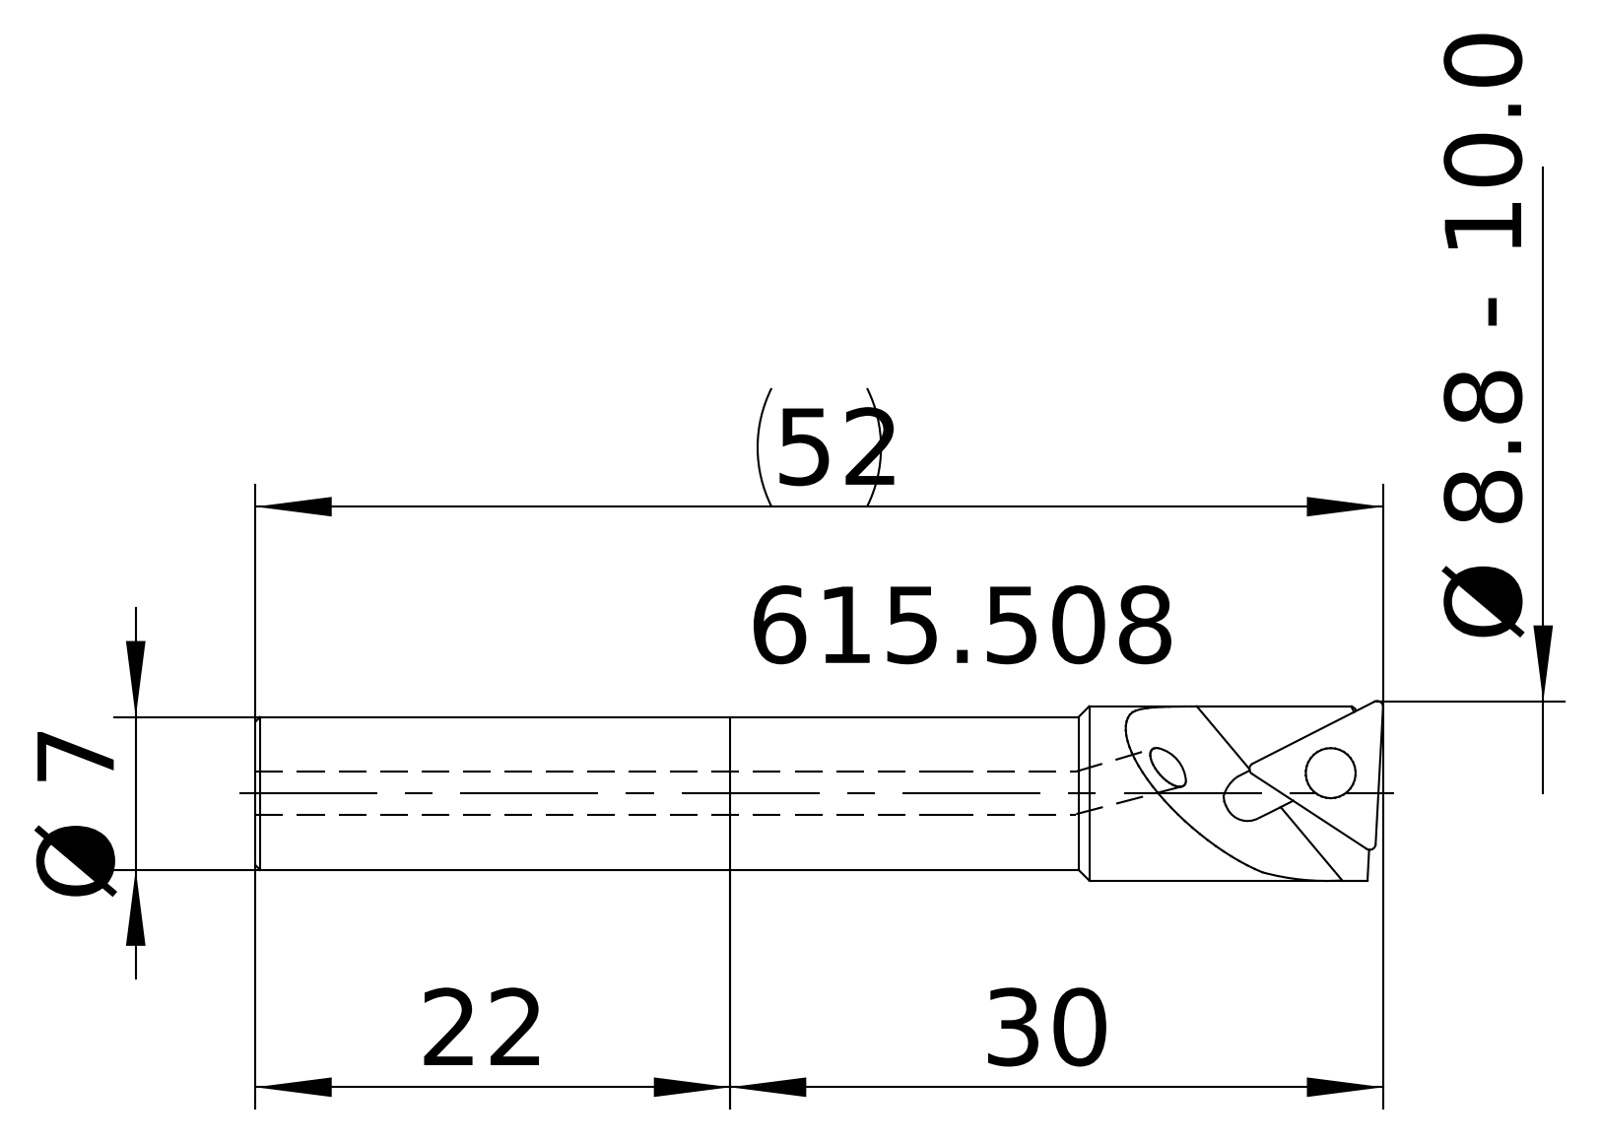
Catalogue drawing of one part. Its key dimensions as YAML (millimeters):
part_name: "615.508 Kaiser E9 TP07 X D7 X 52HM|694.103 Kaiser ETL M2x4.8 T6 IP 10S;Kreismuster1; 615.508 Kaiser E9 TP07 X D7 X 52HM|651.735 Kaiser TPGT 070203 K10C;Kombinieren1; 615.508 Kaiser E9 TP07 X D7 X 52HM|615.508 Kaiser E9 TP07 X D7 X 52HM-1;Fase1; 615.508 Kaiser E9 TP07 X D7 X 52HM|615.508 Kaiser E9 TP07 X D7 X 52HM;<N016.01 (TP 0702) PLS rechts Freistellung links>-<<651.632>-<Kombinieren1>>"
step_written_by: "ACIS (automotive_design)"
units: millimeters
bodies: {solids: 4, faces: 119, planar: 33, cylindrical: 40, other: 46}
overall_size: [51.68, 8.3, 8.24]
volume: 1828
surface_area: 1732
round_holes:
  - {diameter: 2, count: 2}
  - {diameter: 1.56, count: 1}
  - {diameter: 2.3, count: 1}
round_bosses_or_shafts:
  - {diameter: 8, count: 1}
  - {diameter: 7, count: 1}
  - {diameter: 2.7, count: 1}
  - {diameter: 2, count: 1}
partial_cylinders:
  - {radius: 0.15, count: 6}
  - {radius: 0.3, count: 6}
  - {radius: 0.98, count: 1}
  - {radius: 1, count: 1}
  - {radius: 3, count: 1}
face_to_face_distances: [2.5, 2.19, 2.49, 1.72, 0.77, 0.78, 2.31, 4.03, 4.8, 4.81]
